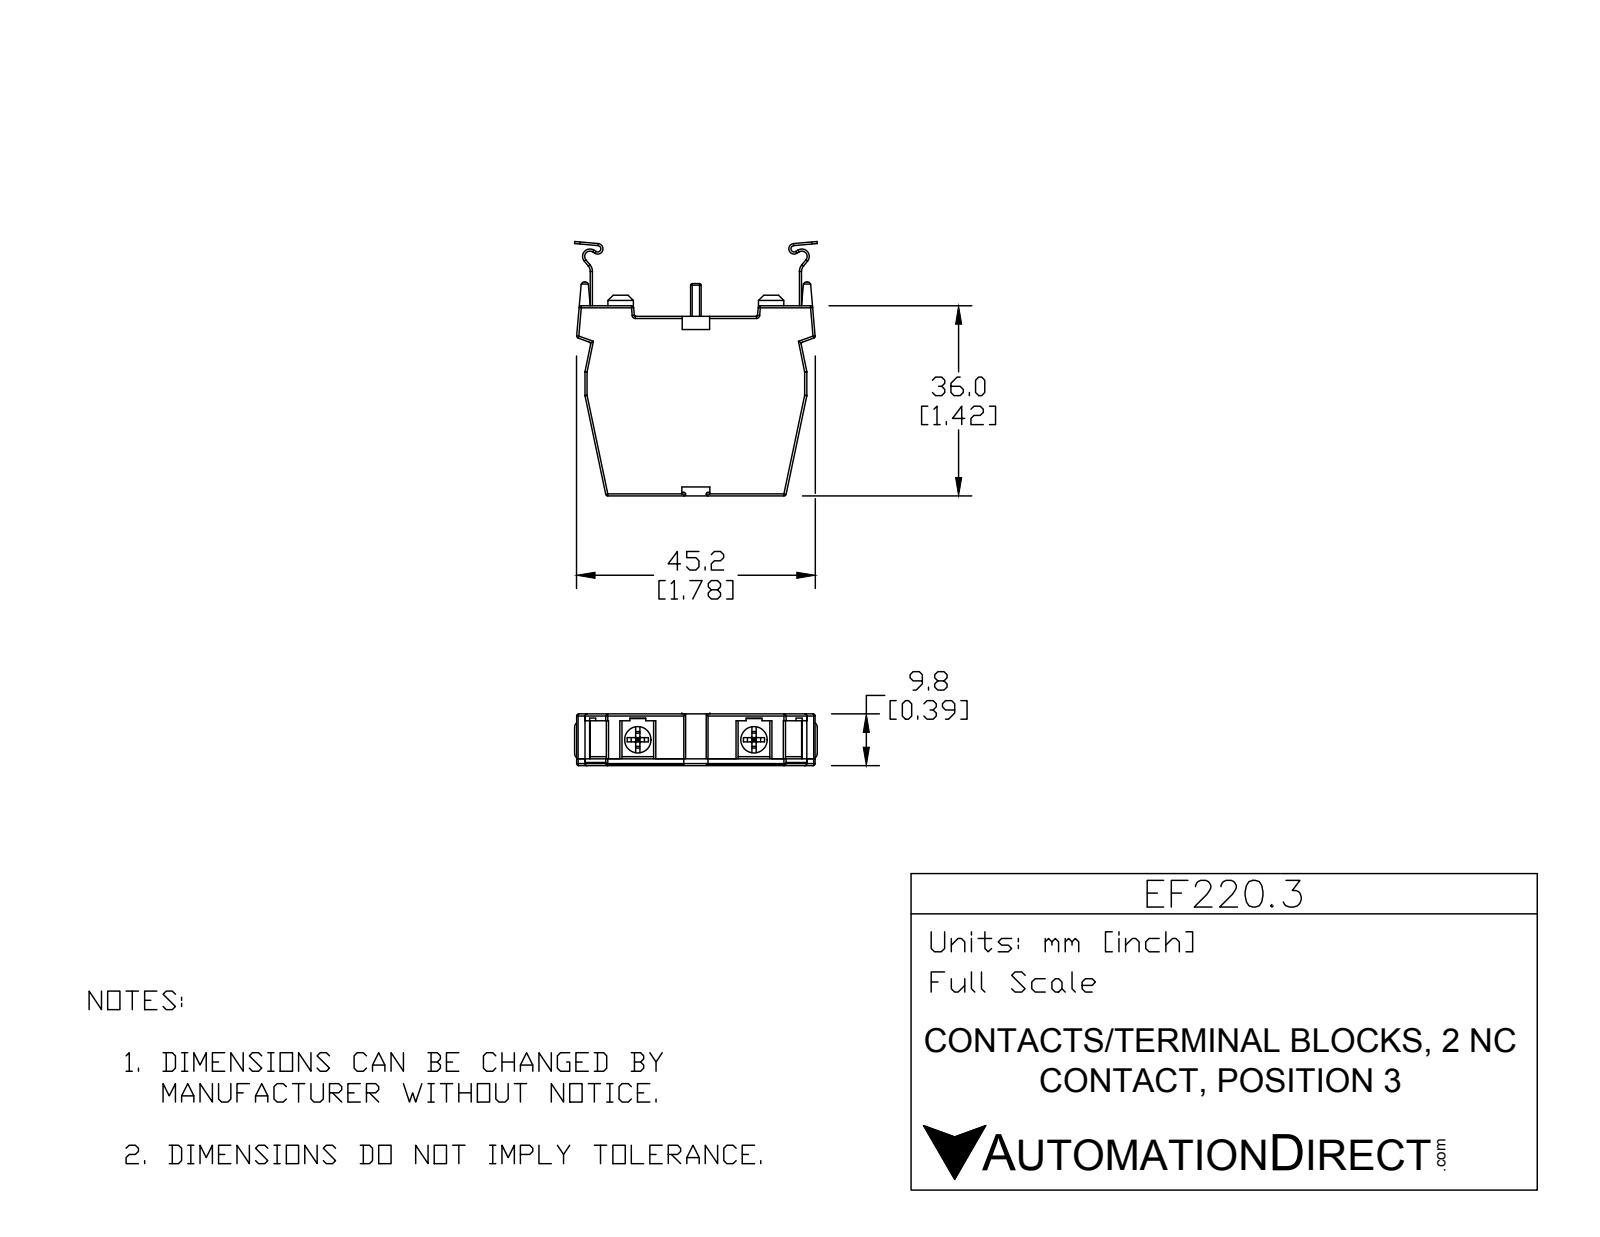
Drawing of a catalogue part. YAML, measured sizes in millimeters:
part_name: "EF220.3"
step_written_by: "SolidWorks 2015 (AUTOMOTIVE_DESIGN)"
units: millimeters
bodies: {solids: 7, faces: 299, planar: 173, cylindrical: 104, other: 22}
overall_size: [48.16, 46.28, 9.8]
volume: 12135
surface_area: 6604
round_holes:
  - {diameter: 5, count: 4}
round_bosses_or_shafts:
  - {diameter: 4, count: 4}
  - {diameter: 4.75, count: 2}
partial_cylinders:
  - {radius: 0.25, count: 44}
  - {radius: 0.5, count: 8}
  - {radius: 1, count: 6}
  - {radius: 0.6, count: 4}
  - {radius: 0.6, count: 2}
  - {radius: 1, count: 2}
  - {radius: 1.4, count: 2}
  - {radius: 1.6, count: 2}
face_to_face_distances: [9.8, 1.4, 8.4, 34, 7, 2, 0.4, 3.18, 37.18, 36]
hole_center_spacings: [21.81]
